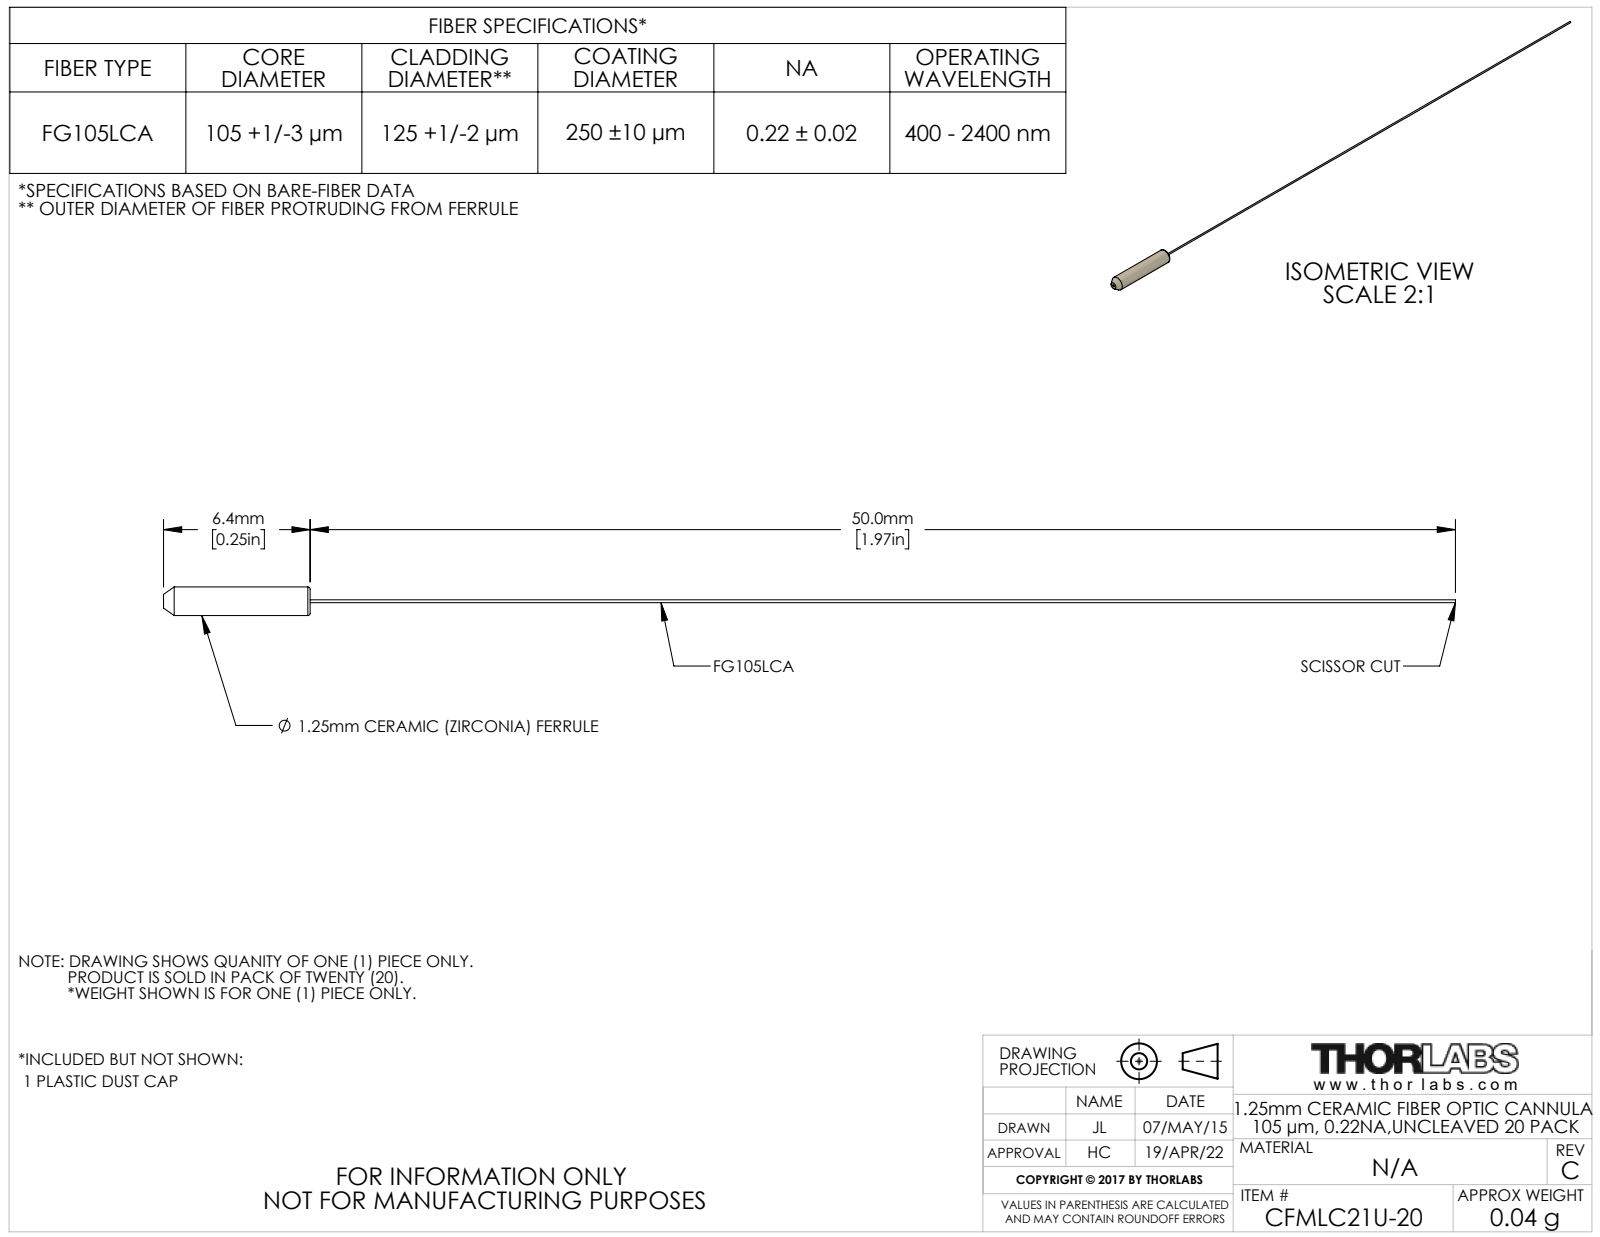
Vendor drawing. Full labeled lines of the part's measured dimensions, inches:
Part name (STEP PRODUCT): TTN041723-E0W
STEP written by: SolidWorks 2014 (CONFIG_CONTROL_DESIGN)
Units: inches
Bodies: 2 solids, 18 faces (4 planar, 6 cylindrical, 8 other)
Overall size (bounding box): 2.22 × 0.049 × 0.049
Round bosses / shafts (diameter × count): ⌀0.049 ×1
Main face-to-face distances: 0.252, 2.22, 1.969
